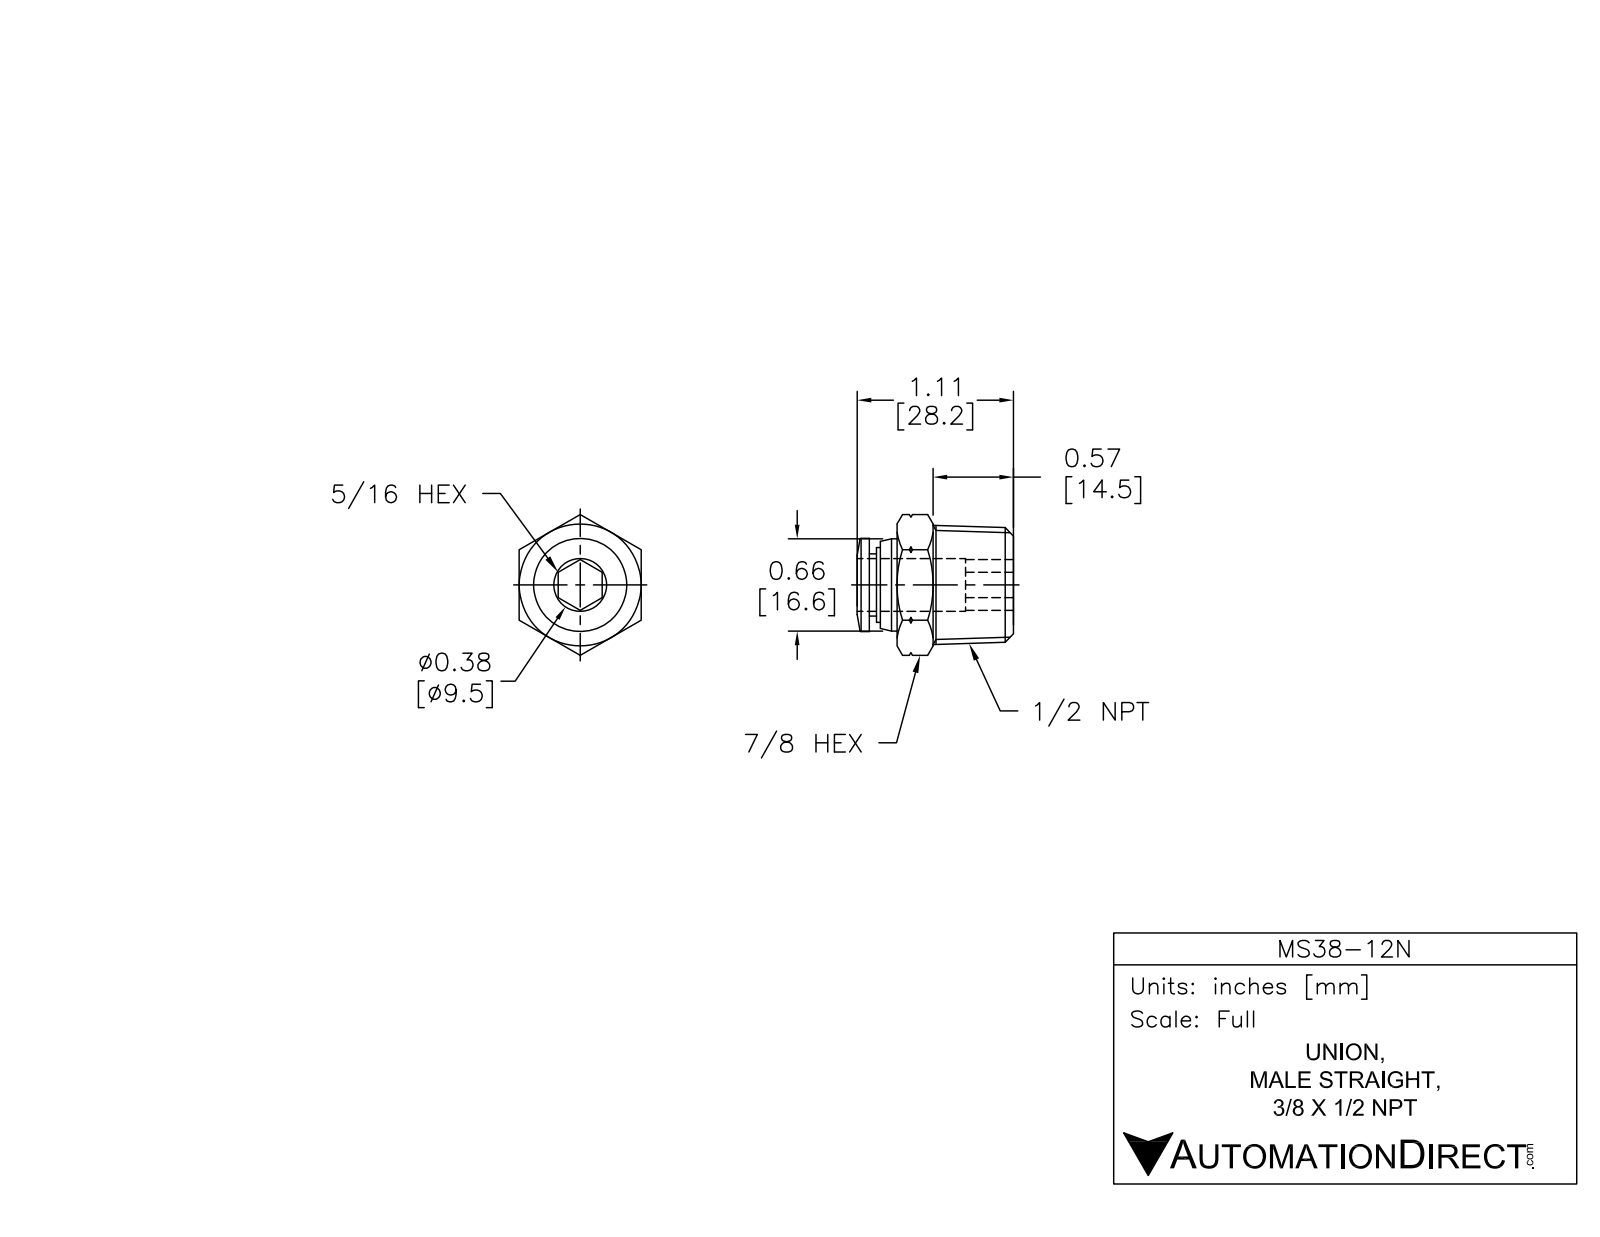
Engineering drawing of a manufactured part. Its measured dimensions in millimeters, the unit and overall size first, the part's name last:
Units: millimetres
Overall size (bounding box): 28.2 × 25.4 × 22
Round holes (diameter × count): ⌀8 ×1, ⌀9.8 ×1
Round bosses / shafts (diameter × count): ⌀16.8 ×1, ⌀16.65 ×1, ⌀13.5 ×1, ⌀11.2 ×1
Main face-to-face distances: 22, 21, 26, 5, 24, 3, 2, 24.7, 3.7, 0.7
Volume: 7 070 mm³ · Surface area: 3 422 mm²
Bodies: 1 solid, 50 faces (13 planar, 6 cylindrical, 31 other)
Part name (STEP PRODUCT): PC3-8--N04
STEP written by: Autodesk Inventor 2008 (AUTOMOTIVE_DESIGN)
